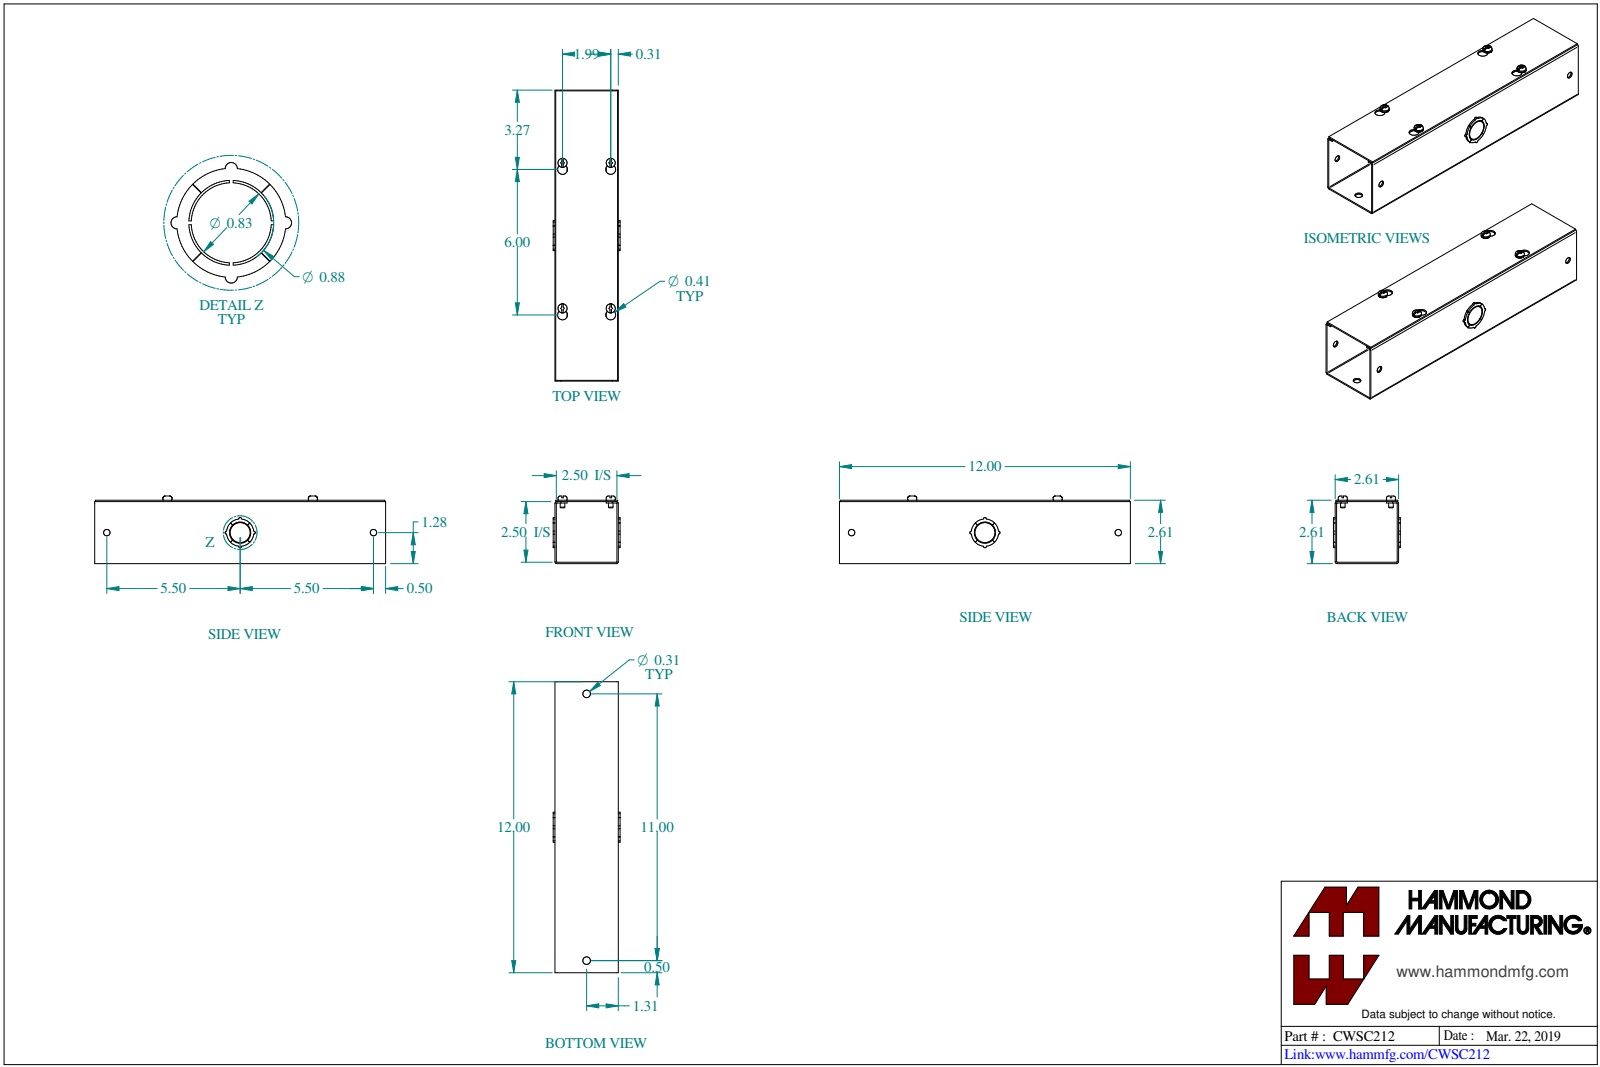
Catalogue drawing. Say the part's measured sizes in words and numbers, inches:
The part is named "CWSC212". Its 3-D file was written by "SolidWorks 2023 (CONFIG_CONTROL_DESIGN)". It is 6 solids with 256 faces: 122 planar, 110 cylindrical and 24 other. Overall it measures 12 by 2.789 by 2.758 inches. Its volume is 7.591 cubic inches and its surface area 266.7 square inches. Round holes: 4 of diameter 0.177, 2 of diameter 0.266, 2 of diameter 0.313, 1 of diameter 0.875. Round bosses or shafts: 4 of diameter 0.375, 4 of diameter 0.19, 1 of diameter 1.125, 1 of diameter 0.825. Partial cylindrical surfaces (rounded edges, fillets, slot ends): 4 of radius 0.029, 4 of radius 0.062, 4 of radius 0.086, 4 of radius 0.125, 4 of radius 0.203. The main face-to-face distances are 0.057, 2.557, 2.5, 2.614, 2.443, 0.114, 0.072, 0.129, 2.629, 2.686. The hole center spacings are 2.691, 8.558, 1.989, 5.5, 6, 6.321, 11.
